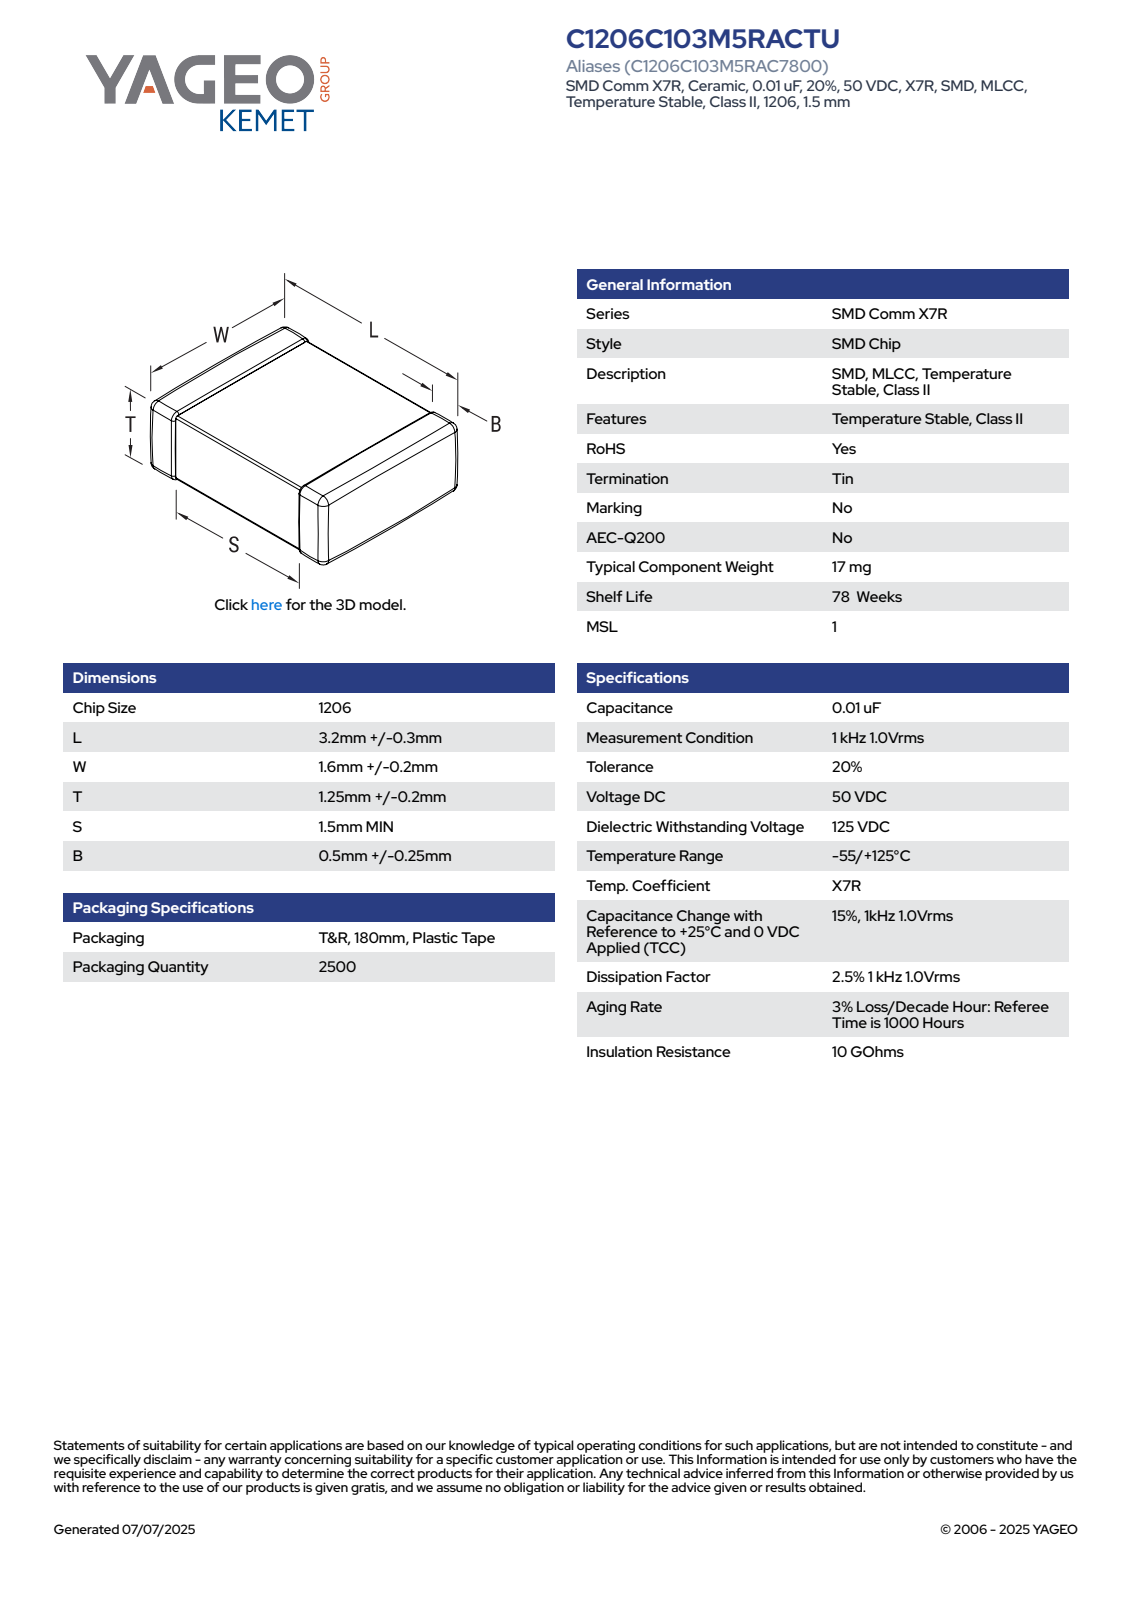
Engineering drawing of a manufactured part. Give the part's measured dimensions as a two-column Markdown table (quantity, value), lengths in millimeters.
| quantity | value |
| --- | --- |
| part name | CCS_CCSTD_1206_L3.5W1.8T1.45B0.5 |
| STEP written by | SolidWorks 2021 (AUTOMOTIVE_DESIGN) |
| units | millimeters |
| bodies | 4 solids, 125 faces (71 planar, 38 cylindrical, 16 other) |
| overall size | 3.5 × 1.8 × 1.45 |
| volume | 9 mm³ |
| surface area | 28 mm² |
| main face-to-face distances | 1.41, 1.76, 1.37, 1.72, 3.5, 1.45, 1.8, 1.42, 1.38, 1.63 |
